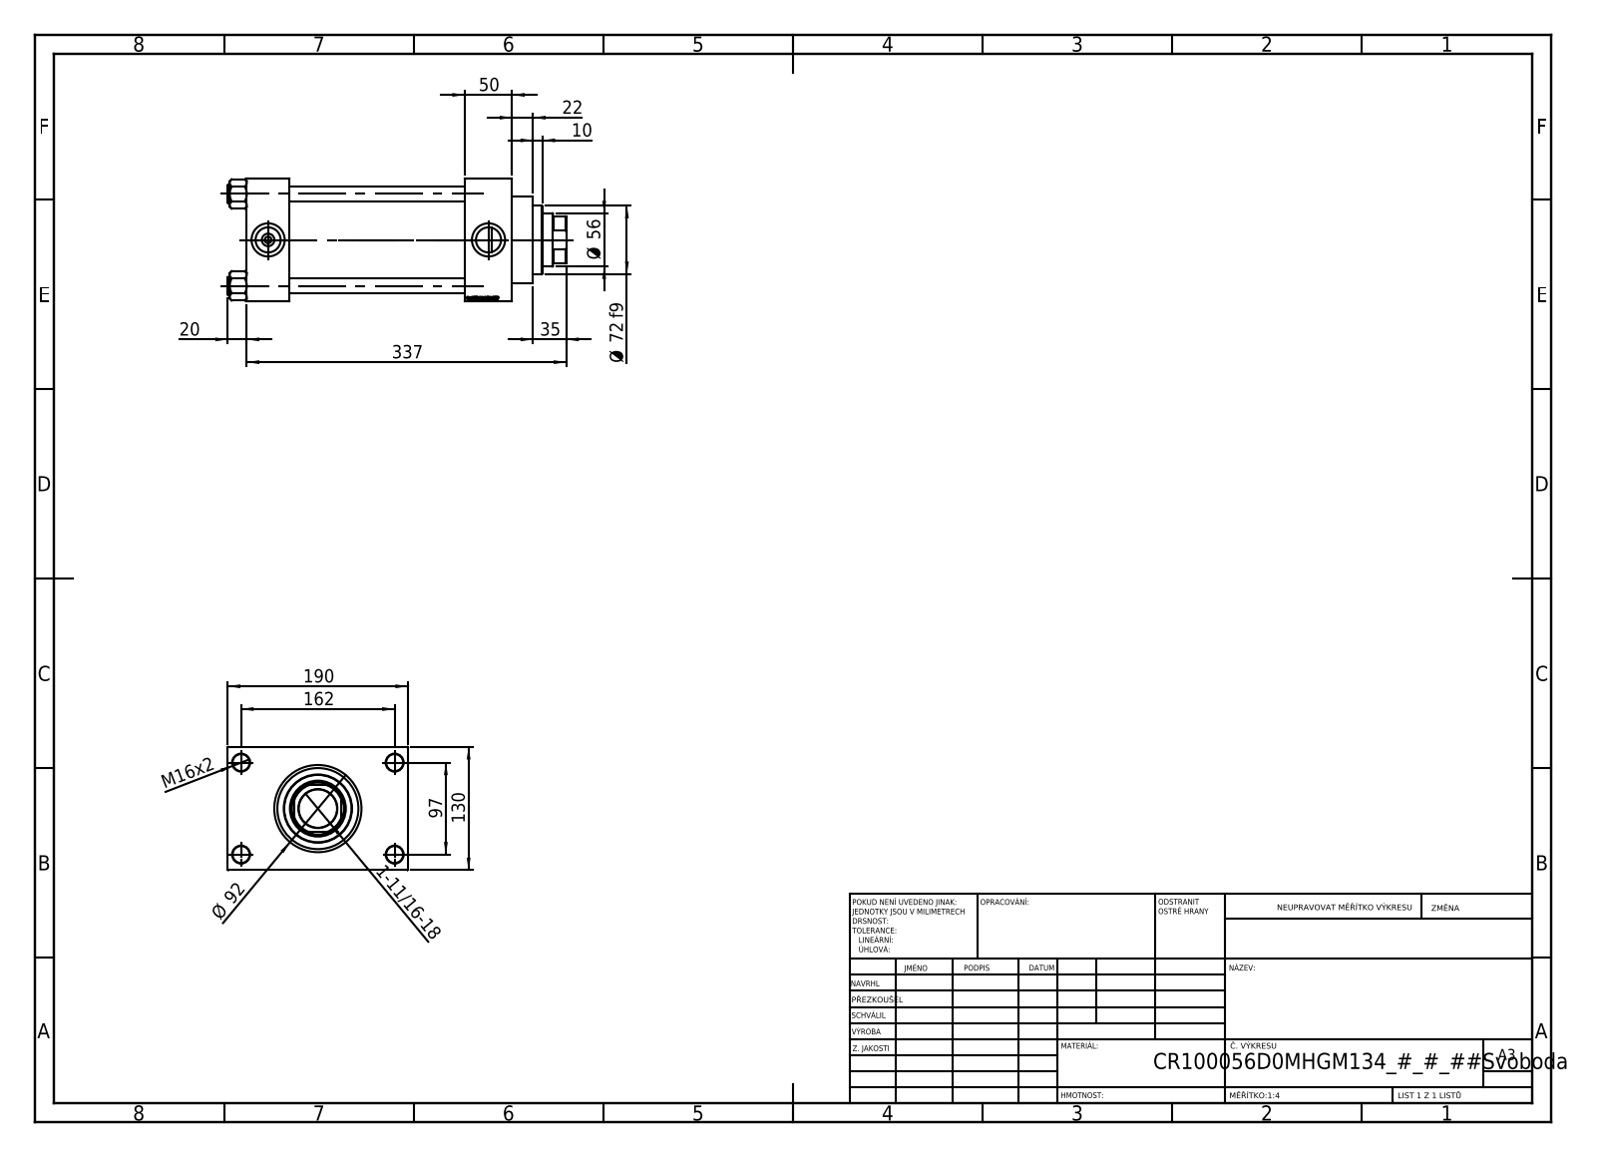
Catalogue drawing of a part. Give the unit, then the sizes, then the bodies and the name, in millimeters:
Units: millimetres
Overall size (bounding box): 357 × 190 × 130
Round holes (diameter × count): ⌀16 ×4, ⌀18 ×4, ⌀7 ×2, ⌀26.44 ×2, ⌀35 ×2, ⌀40.5 ×1, ⌀56 ×1, ⌀59 ×1, ⌀76 ×1, ⌀85.5 ×1, ⌀100 ×1
Round bosses / shafts (diameter × count): ⌀19 ×4, ⌀106 ×1, ⌀92 ×1, ⌀72 ×1
Partial cylindrical surfaces — rounded edges, fillets, slot ends (radius × count): R27 ×1
Main face-to-face distances: 130, 50, 45, 185, 230, 280, 235, 30, 160, 190
Hole centre spacings: 32.55, 68.52, 94.41, 96.9, 102.27, 129.45, 161.73, 97
Volume: 3 111 000 mm³ · Surface area: 479 117 mm²
Bodies: 11 solids, 1151 faces (545 planar, 88 cylindrical, 518 other)
Part name (STEP PRODUCT): V215CR_D_TYCINKA; V215CR_VCP_D; NUT_M5_D; V215_VC_A (+1 more)
STEP written by: SolidWorks 2019 (CONFIG_CONTROL_DESIGN)
